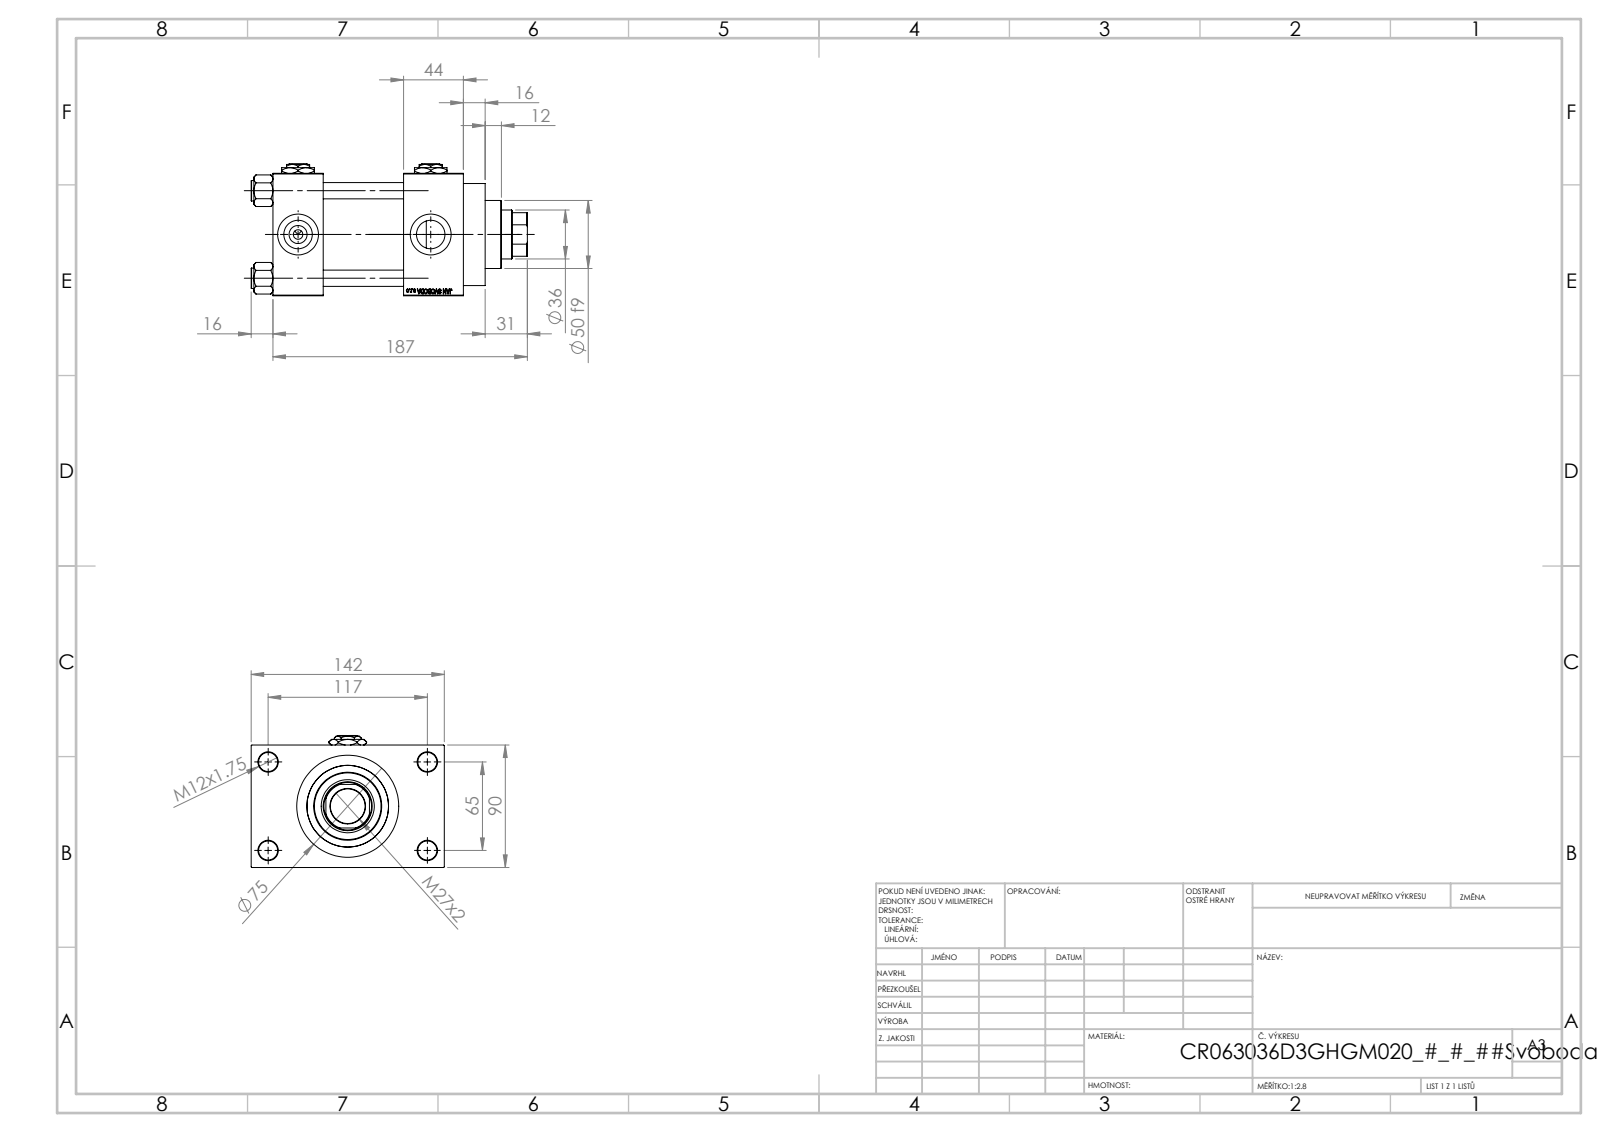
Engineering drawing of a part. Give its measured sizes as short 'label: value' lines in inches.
name: V215_VC_A; V215CR_D_TYCINKA; V215CR_VCP_D; NUT_M5_D (+2 more)
written by: SolidWorks 2019 (CONFIG_CONTROL_DESIGN)
unit: in
bodies: 13 solids, 1204 faces (545 planar, 99 cylindrical, 560 other)
size: 7.992 × 5.591 × 3.819
volume: 67.49 in³; area: 326.1 in²
holes: 4× ⌀0.472, 4× ⌀0.551, 4× ⌀0.825, 4× ⌀1.181, 3× ⌀0.276, 1× ⌀1.004, 1× ⌀1.417, 1× ⌀1.535, 1× ⌀1.969, 1× ⌀2.362, 1× ⌀2.48
bosses: 4× ⌀0.591, 1× ⌀2.953, 1× ⌀2.717
rounds: 1× R0.689
face distances: 3.543, 2.323, 1.457, 3.78, 5.512, 4.055, 1.732, 1.024, 4.567, 5.591
hole spacings: 1.037, 1.79, 2.531, 2.635, 2.748, 3.569, 4.383, 2.559
